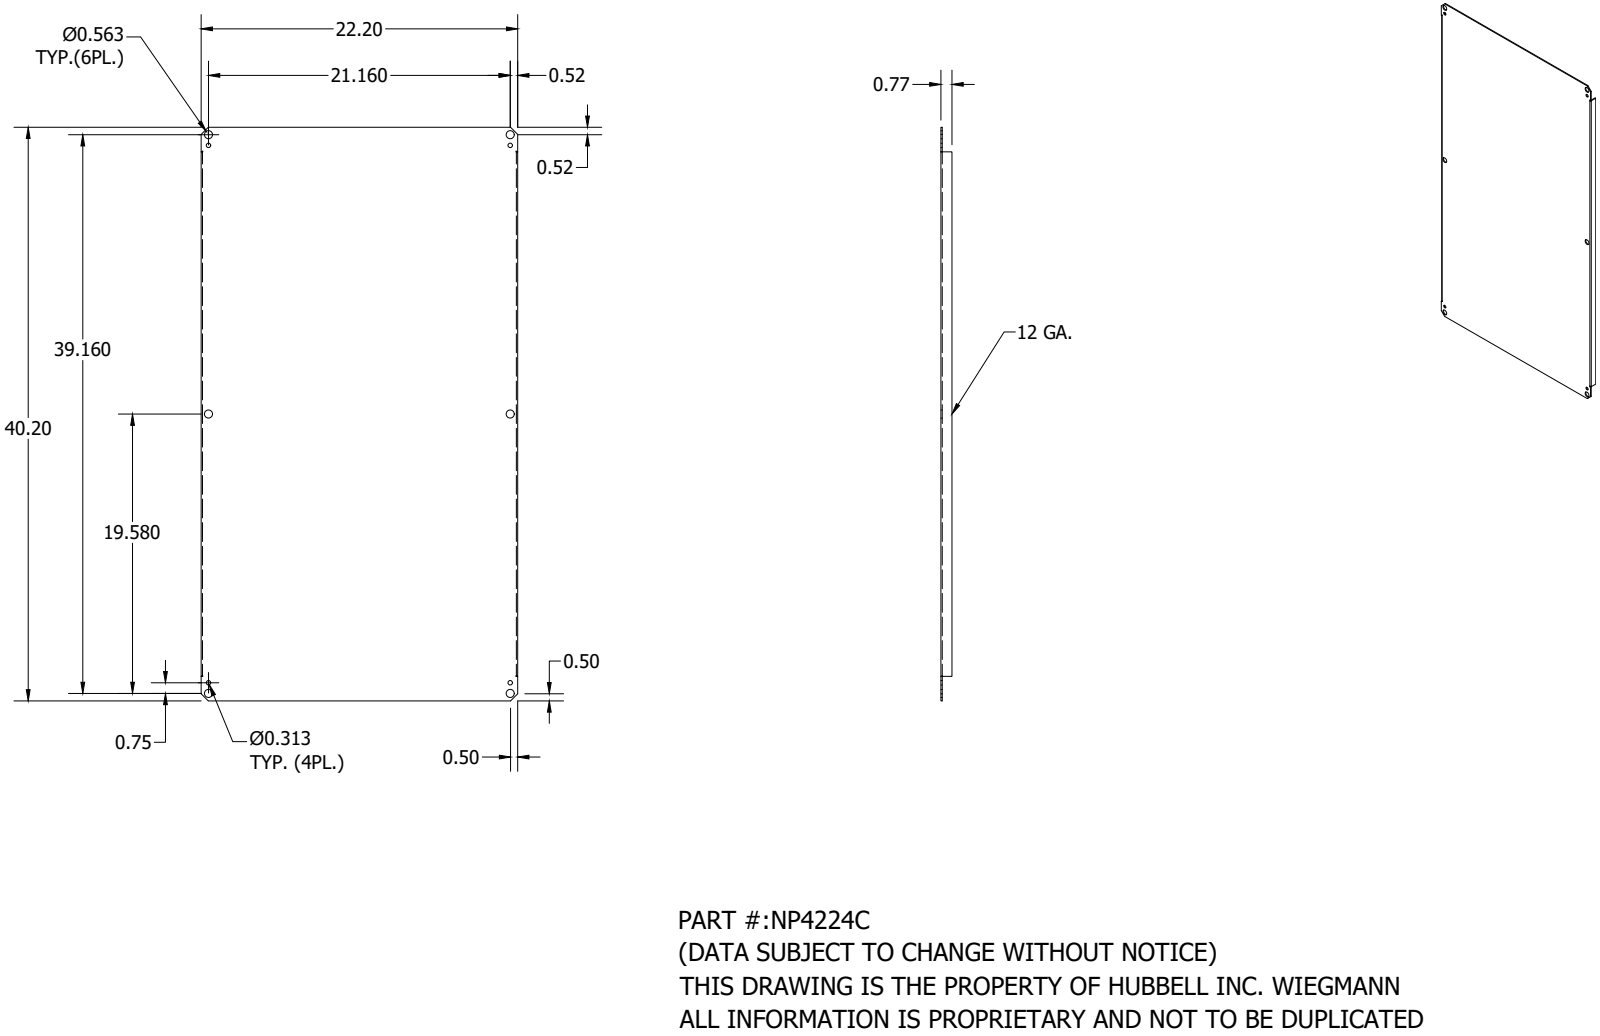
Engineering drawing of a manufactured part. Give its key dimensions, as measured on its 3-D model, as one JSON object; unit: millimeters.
{"part_name": "NP4224C", "step_written_by": "Autodesk Inventor 2018 (AUTOMOTIVE_DESIGN)", "units": "millimeters", "bodies": {"solids": 1, "faces": 44, "planar": 30, "cylindrical": 14, "other": 0}, "overall_size": [1021.1, 563.9, 19.7], "volume_mm3": 1441000, "surface_area_mm2": 1219000, "round_holes": [[14.3, 6], [8, 4]], "partial_cylinders_radius": [[0.4, 2], [2.8, 2]], "face_to_face_distances": [2.4, 561.5, 563.9, 559.1, 17.3, 19.7, 1021.1, 43.6, 977.4, 933.8], "hole_center_spacings": [537.5, 19.1, 478.3, 497.3, 537.8, 719.5, 732.3, 975.6]}
